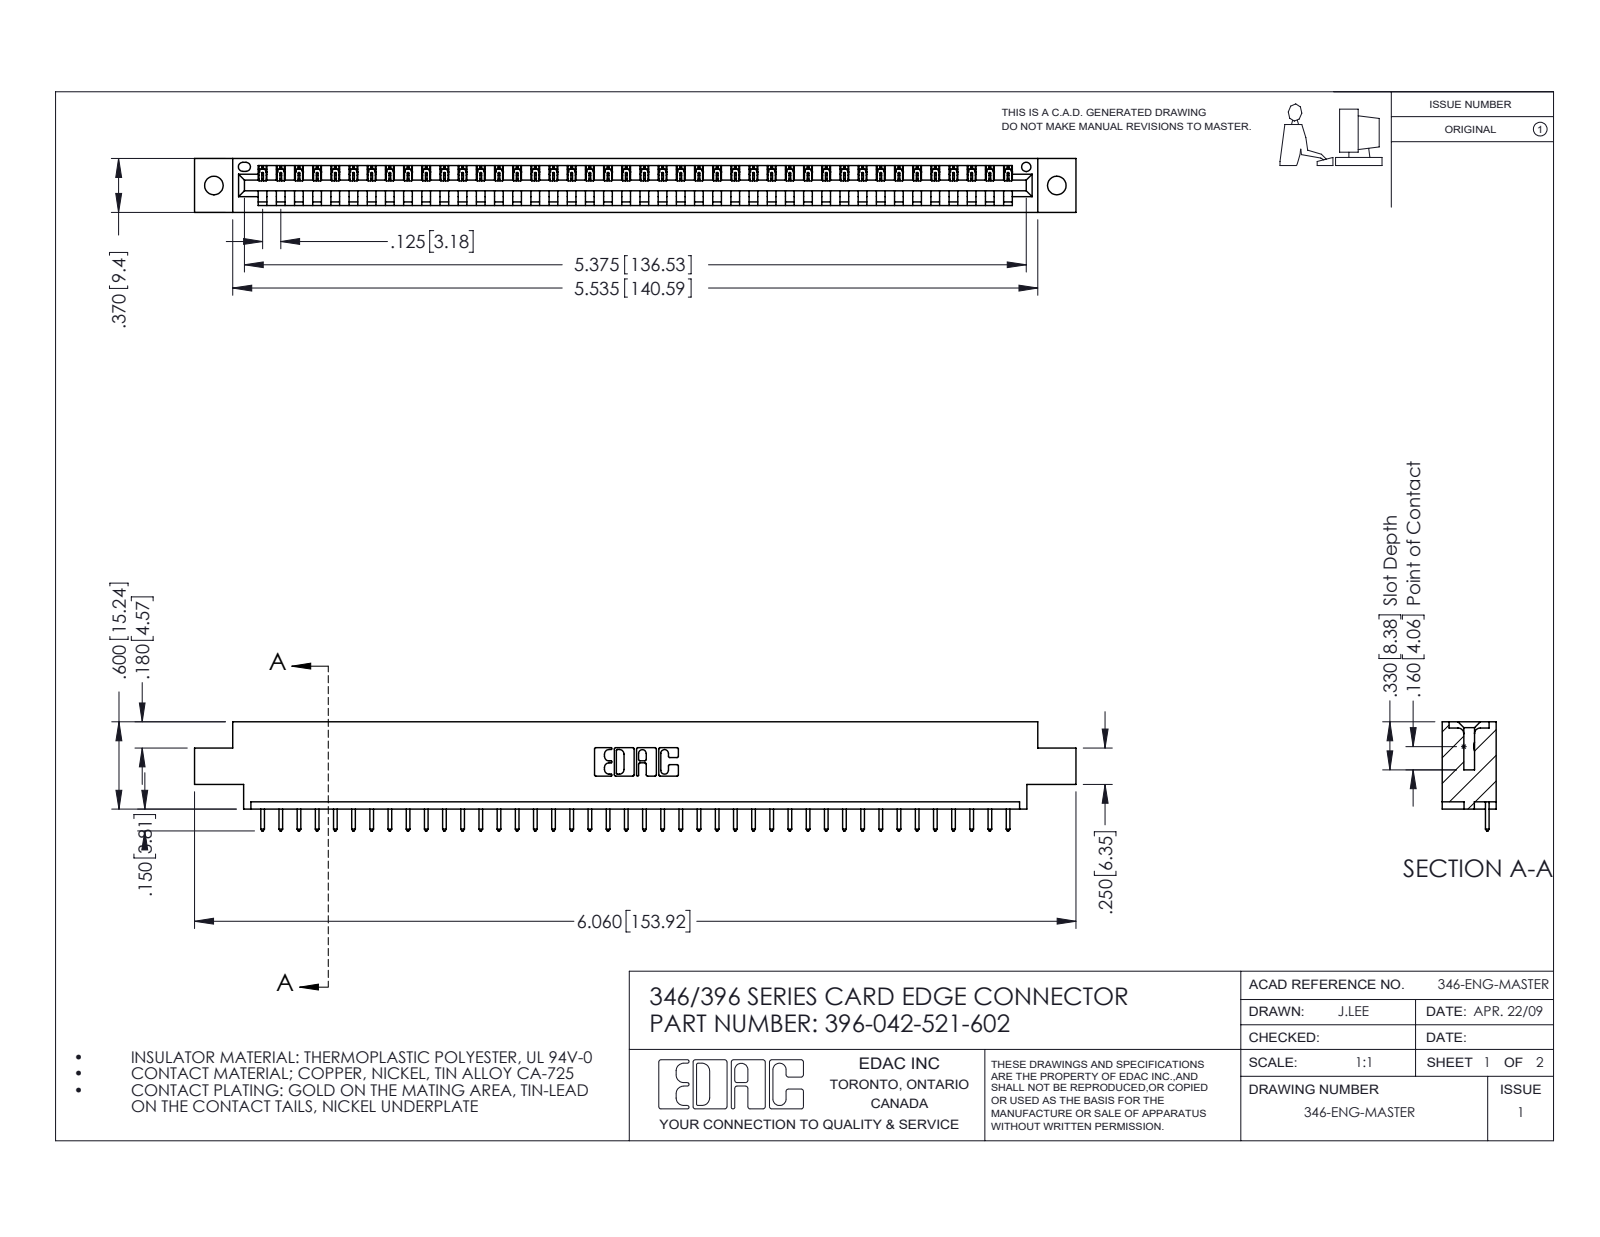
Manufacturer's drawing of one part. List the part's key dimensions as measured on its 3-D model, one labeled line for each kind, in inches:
Part name (STEP PRODUCT): 396-042-521-602; 345-292-001_345-293-121; 346 Part_0.170 Offset - 0.128 Dia
STEP written by: SolidWorks 2016 (CONFIG_CONTROL_DESIGN)
Units: inches
Bodies: 43 solids, 2562 faces (1760 planar, 802 cylindrical, 0 other)
Overall size (bounding box): 6.06 × 0.75 × 0.37
Volume: 0.88 in³ · Surface area: 27.03 in²
Round holes (diameter × count): ⌀0.128 ×2, ⌀0.064 ×1
Partial cylindrical surfaces — rounded edges, fillets, slot ends (radius × count): R0.006 ×84, R0.01 ×84, R0.01 ×22, R0.007 ×6, R0.031 ×6, R0.026 ×3, R0.031 ×2, R0.04 ×2
Main face-to-face distances: 0.048, 0.322, 0.37, 0.25, 0.072, 0.298, 0.025, 0.148, 0.222, 0.1
Hole centre spacings: 0.246, 5.586, 5.795
